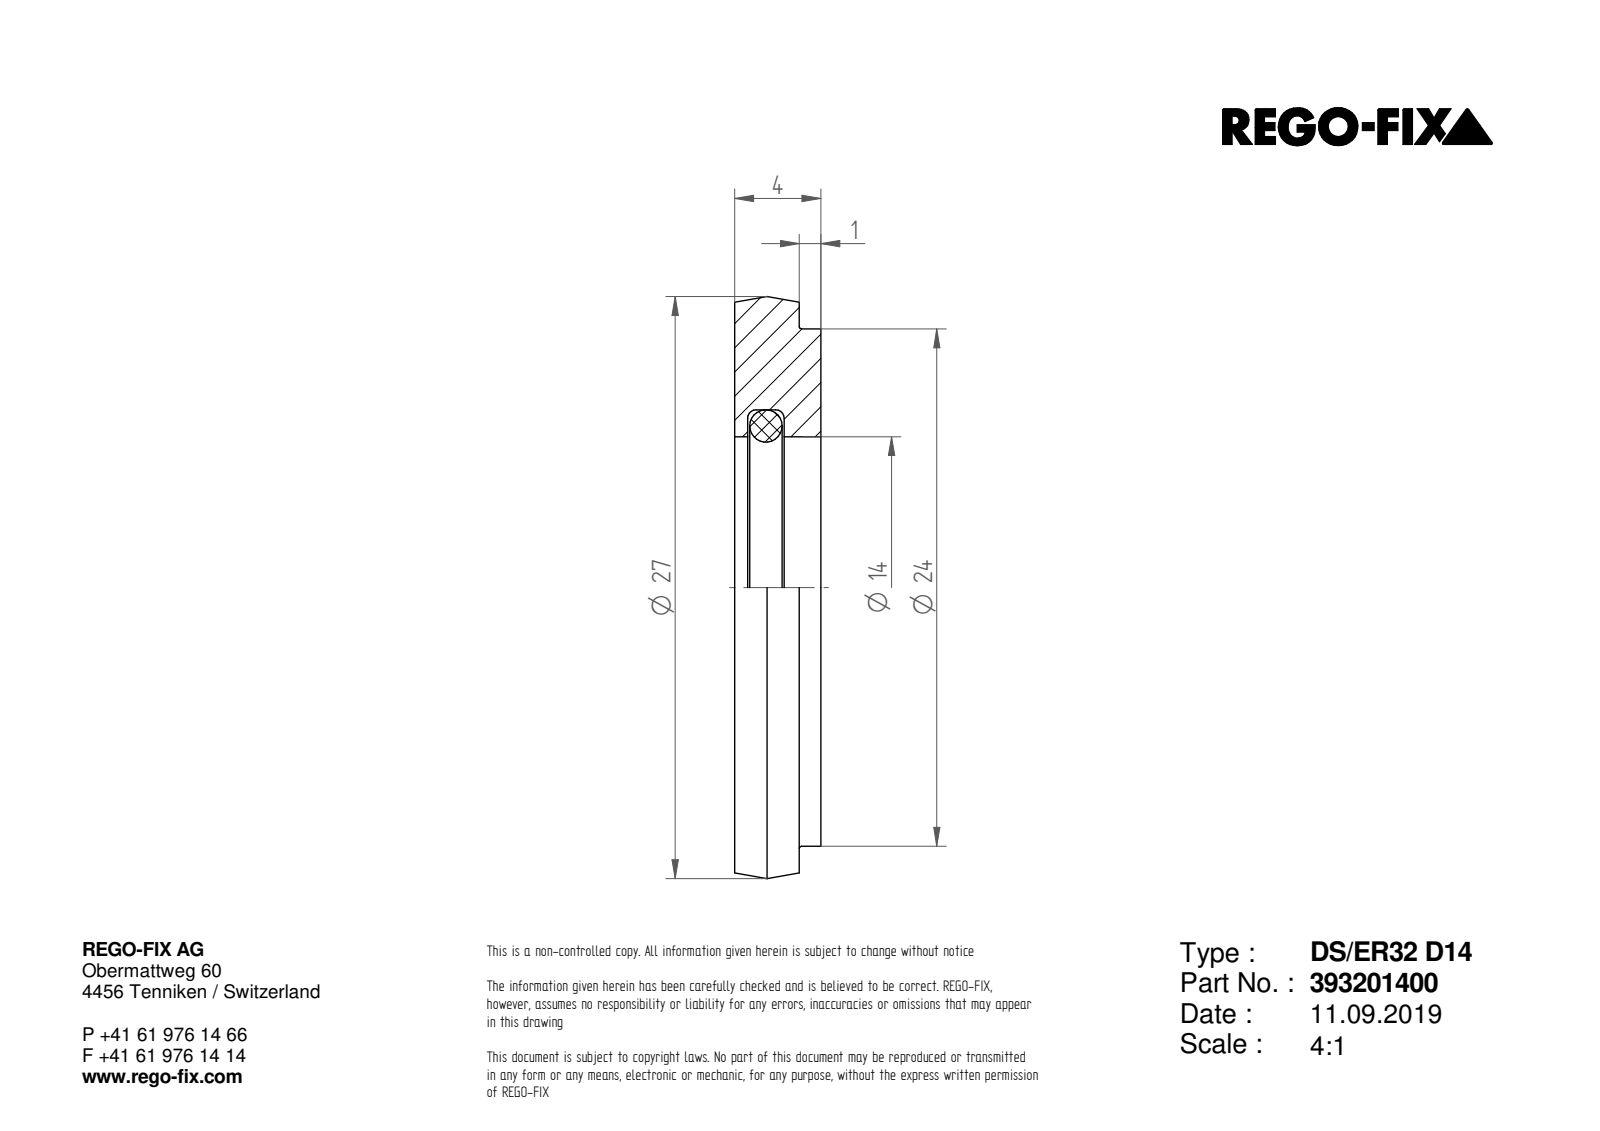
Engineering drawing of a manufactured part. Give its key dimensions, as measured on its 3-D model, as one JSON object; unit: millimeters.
{"part_name": "NOCUT", "step_written_by": "SIEMENS PLM Software Solid Edge ST10 (AUTOMOTIVE_DESIGN)", "units": "millimeters", "bodies": {"solids": 1, "faces": 7, "planar": 3, "cylindrical": 3, "other": 1}, "overall_size": [27, 27, 4], "volume_mm3": 1554, "surface_area_mm2": 1340, "round_holes": [[14, 1]], "round_bosses_or_shafts": [[27, 1], [24, 1]], "face_to_face_distances": [4, 1, 3]}
